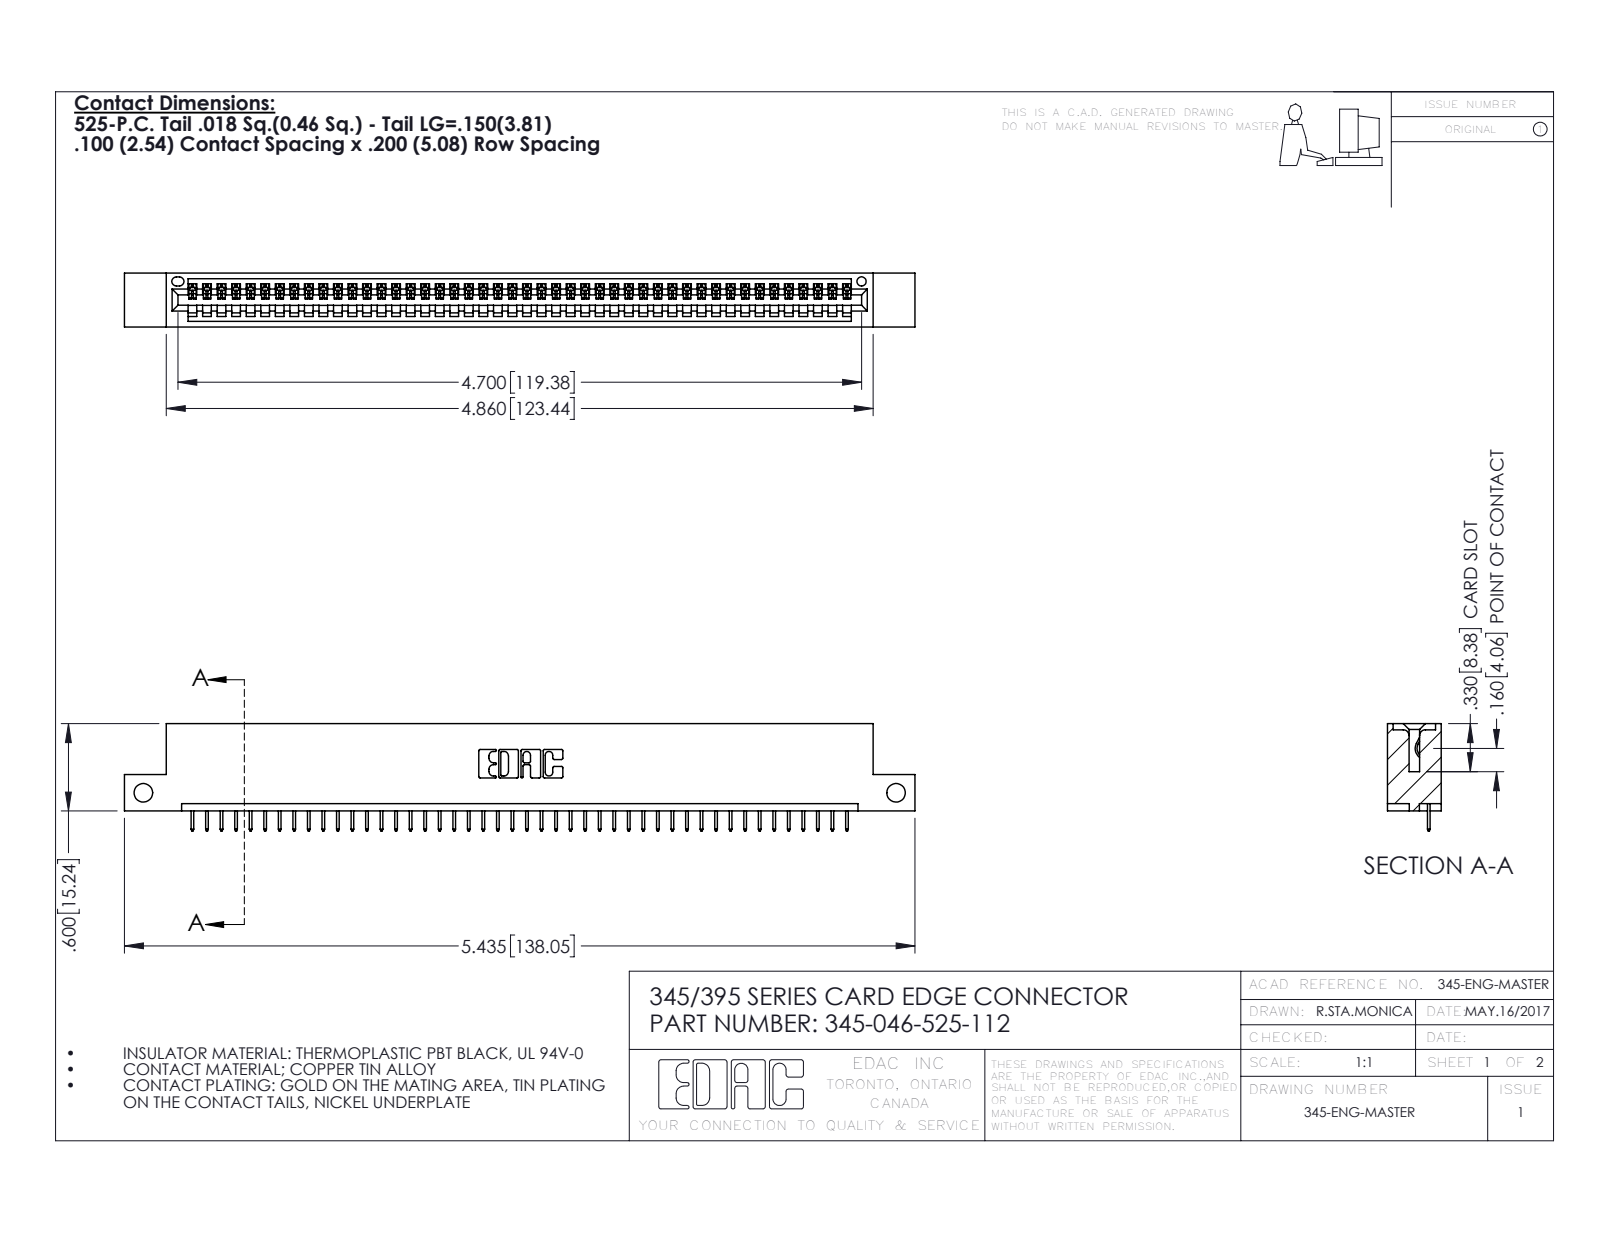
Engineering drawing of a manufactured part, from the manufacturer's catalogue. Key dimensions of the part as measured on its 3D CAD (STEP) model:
Part name (STEP PRODUCT): 345 Part_Flush Mounting Lugs - Side Mount; 345-292-001_345-293-125; 345-046-525-112
STEP written by: SolidWorks 2020 (CONFIG_CONTROL_DESIGN)
Units: inches
Bodies: 47 solids, 2978 faces (2196 planar, 782 cylindrical, 0 other)
Overall size (bounding box): 5.435 × 0.737 × 0.37
Volume: 0.785 in³ · Surface area: 25.4 in²
Round holes (diameter × count): ⌀0.128 ×2, ⌀0.064 ×1
Partial cylindrical surfaces — rounded edges, fillets, slot ends (radius × count): R0.006 ×92, R0.01 ×22, R0.007 ×6, R0.031 ×6, R0.026 ×3, R0.031 ×2, R0.04 ×2, R0.014 ×1
Main face-to-face distances: 0.298, 0.072, 0.37, 0.2, 0.098, 0.272, 0.025, 0.225, 0.072, 0.149
Hole centre spacings: 5.175
